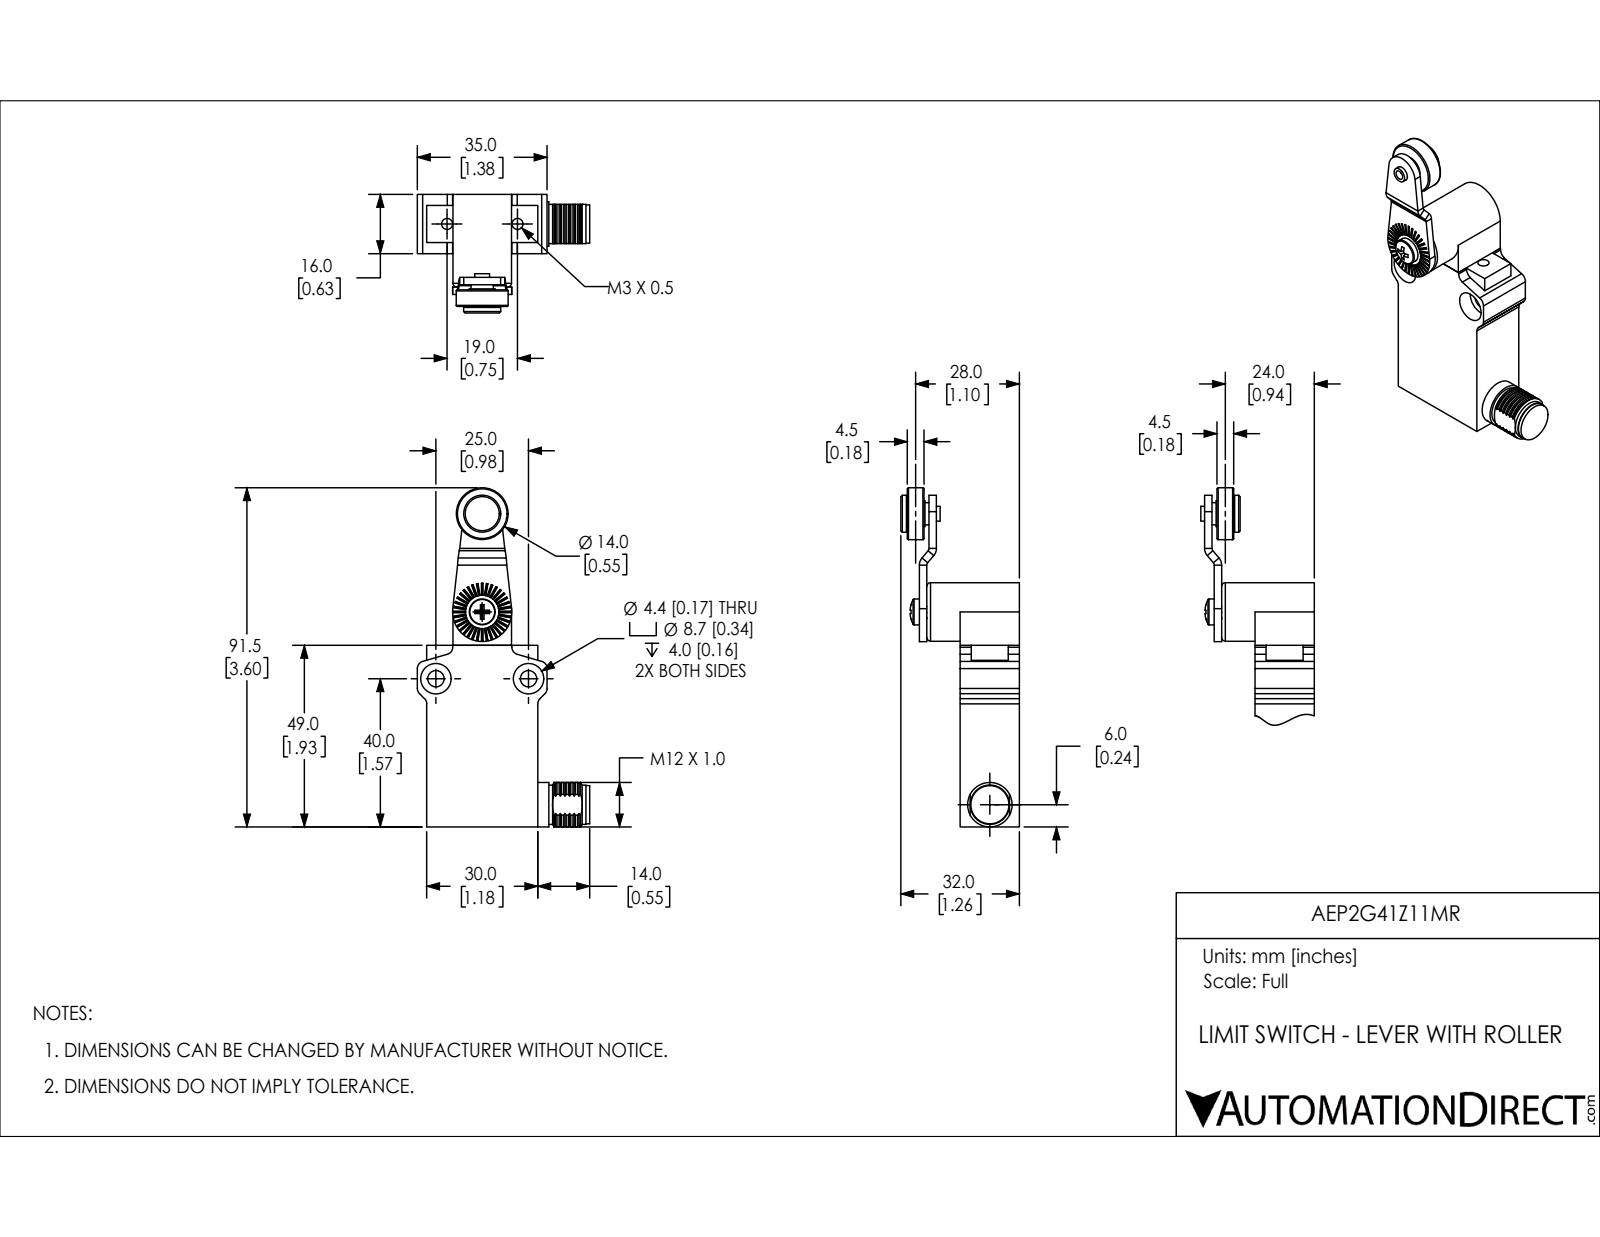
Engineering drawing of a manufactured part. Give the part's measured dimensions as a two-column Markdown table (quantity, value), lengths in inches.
| quantity | value |
| --- | --- |
| part name | AEP2G41Z11MR |
| STEP written by | SolidWorks 2018 (AUTOMOTIVE_DESIGN) |
| units | inches |
| bodies | 7 solids, 657 faces (299 planar, 146 cylindrical, 212 other) |
| overall size | 3.602 × 1.831 × 1.26 |
| volume | 1.899 in³ |
| surface area | 18.2 in² |
| round holes (diameter × count) | 0.118 × 2, 0.173 × 2, 0.197 × 2, 0.323 × 2, 0.098 × 1, 0.161 × 1, 0.224 × 1 |
| round bosses / shafts (diameter × count) | 0.276 × 2, 0.622 × 1, 0.551 × 1, 0.472 × 1, 0.417 × 1, 0.406 × 1, 0.394 × 1, 0.236 × 1 |
| partial cylindrical surfaces (radius × count) | 0.079 × 8, 0.039 × 2, 0.118 × 2, 0.256 × 1, 0.315 × 1 |
| main face-to-face distances | 0.63, 1.181, 1.929, 0.354, 0.079, 0.984, 0.28, 0.902, 0.102, 0.472 |
| hole center spacings | 0.863, 1.82, 0.748, 0.984, 1.043 |
